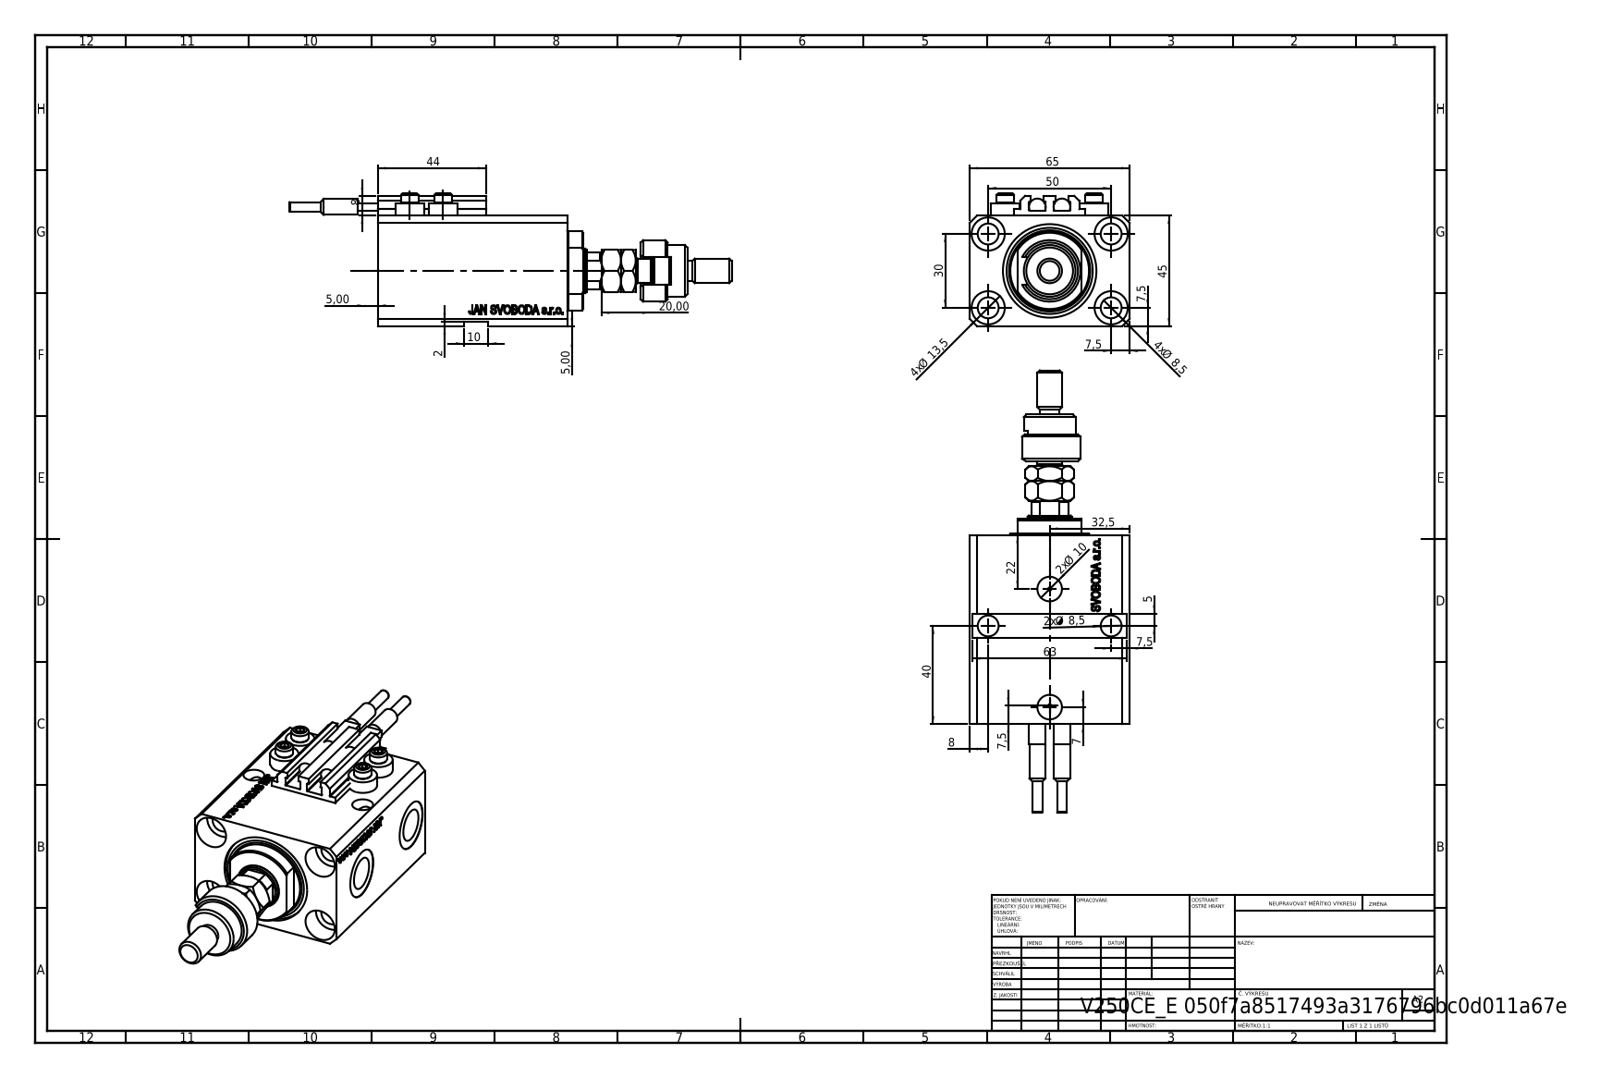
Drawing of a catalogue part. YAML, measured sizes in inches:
part_name: "FEMALE_PART_FOR_DFA; V250CE_VC_E; ALLEN BOLT V250CE; V250CE_C_VCP (+3 more)"
step_written_by: "SolidWorks 2019 (CONFIG_CONTROL_DESIGN)"
units: inches
bodies: {solids: 12, faces: 1204, planar: 571, cylindrical: 151, other: 482}
overall_size: [7.083, 2.559, 2.126]
volume: 13.13
surface_area: 107.7
round_holes:
  - {diameter: 0.335, count: 7}
  - {diameter: 0.049, count: 4}
  - {diameter: 0.157, count: 4}
  - {diameter: 0.531, count: 4}
  - {diameter: 0.394, count: 2}
  - {diameter: 0.518, count: 2}
  - {diameter: 0.787, count: 2}
  - {diameter: 0.709, count: 1}
  - {diameter: 1.496, count: 1}
round_bosses_or_shafts:
  - {diameter: 0.457, count: 4}
  - {diameter: 0.276, count: 4}
  - {diameter: 0.268, count: 2}
  - {diameter: 0.256, count: 2}
  - {diameter: 0.157, count: 2}
  - {diameter: 0.984, count: 1}
  - {diameter: 0.827, count: 1}
  - {diameter: 0.63, count: 1}
partial_cylinders:
  - {radius: 0.008, count: 10}
  - {radius: 0.217, count: 1}
  - {radius: 0.335, count: 1}
  - {radius: 0.344, count: 1}
  - {radius: 0.63, count: 1}
face_to_face_distances: [1.772, 2.559, 2.043, 0.079, 0.988, 0.118, 3.031, 0.272, 1.85, 2.76]
hole_center_spacings: [1.148, 1.969, 0.535, 0.595, 0.741, 0.747, 1.032, 1.048]
